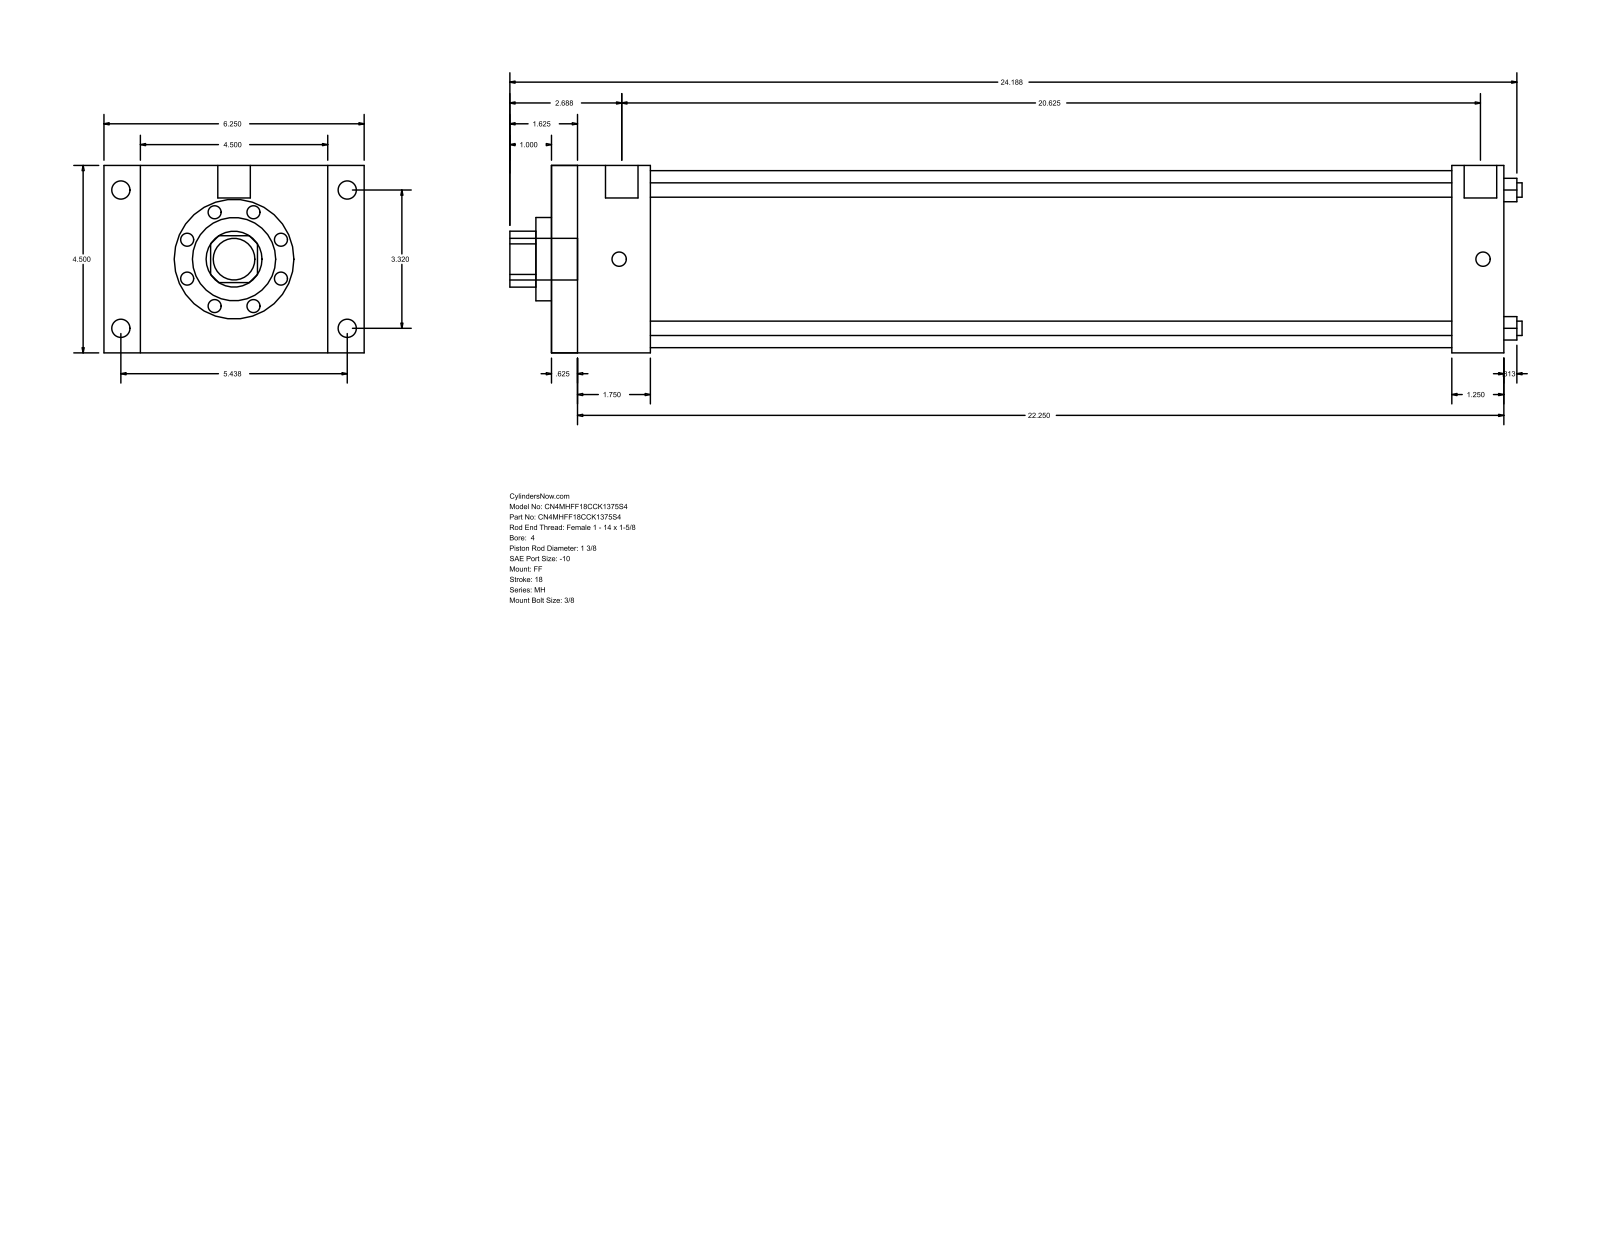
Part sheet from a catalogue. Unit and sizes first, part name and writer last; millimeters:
Units: millimetres
Overall size (bounding box): 617.54 × 158.75 × 114.3
Round holes (diameter × count): ⌀8.76 ×4, ⌀34.92 ×1, ⌀50.8 ×1, ⌀107.95 ×1
Round bosses / shafts (diameter × count): ⌀11.13 ×4, ⌀8.73 ×4, ⌀19.84 ×2, ⌀25.4 ×1
Partial cylindrical surfaces — rounded edges, fillets, slot ends (radius × count): R17.06 ×1
Main face-to-face distances: 114.3, 581.02, 15.87, 565.15, 60.32, 44.45, 520.7, 549.27, 533.4, 488.95
Hole centre spacings: 59.62, 84.32, 119.25
Bodies: 0 solids, 92 faces (64 planar, 28 cylindrical, 0 other)
Part name (STEP PRODUCT): MH_FF__0400_1.375
STEP written by: GSSL Pune (CONFIG_CONTROL_DESIGN)
